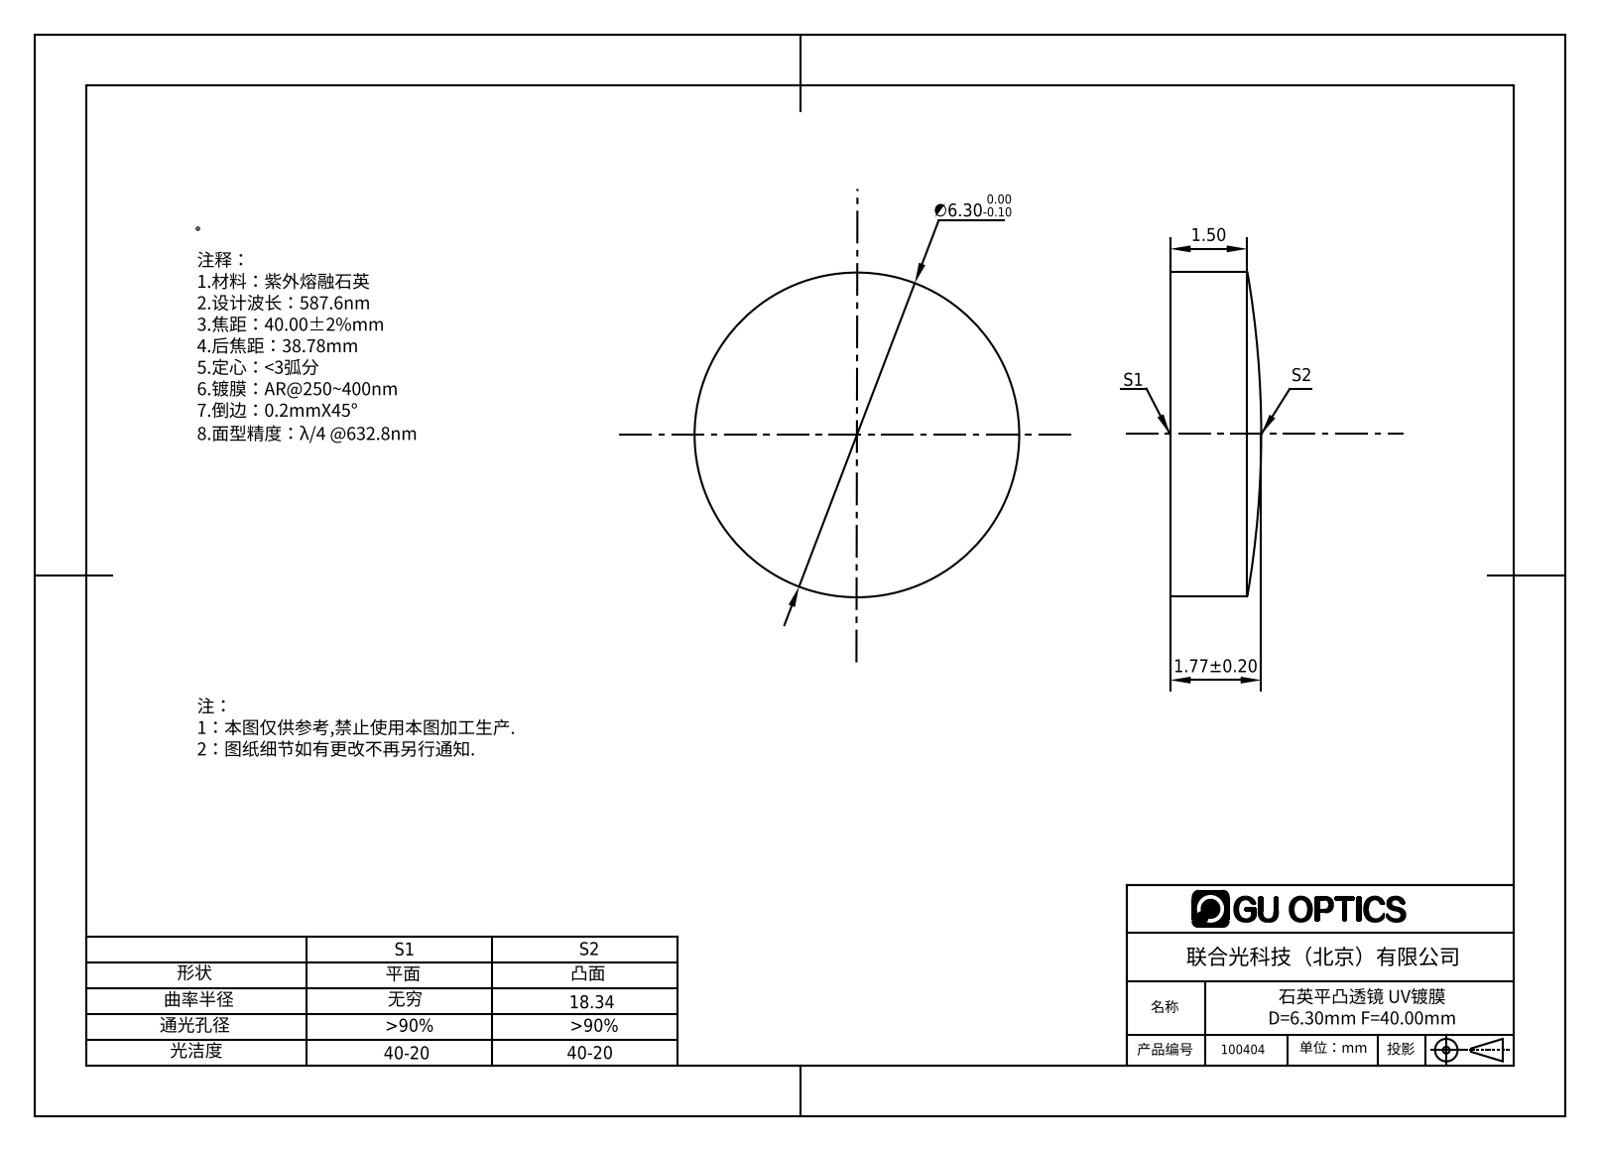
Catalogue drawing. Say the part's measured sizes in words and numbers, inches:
The part is named "100354". Its 3-D file was written by "SolidWorks 2016 (AUTOMOTIVE_DESIGN)". It is 1 solid with 5 faces: 1 planar, 2 cylindrical and 2 other. Overall it measures 0.248 by 0.248 by 0.07 inches. Its volume is 0.003 cubic inches and its surface area 0.14 square inches. Round bosses or shafts: 1 of diameter 0.248.
